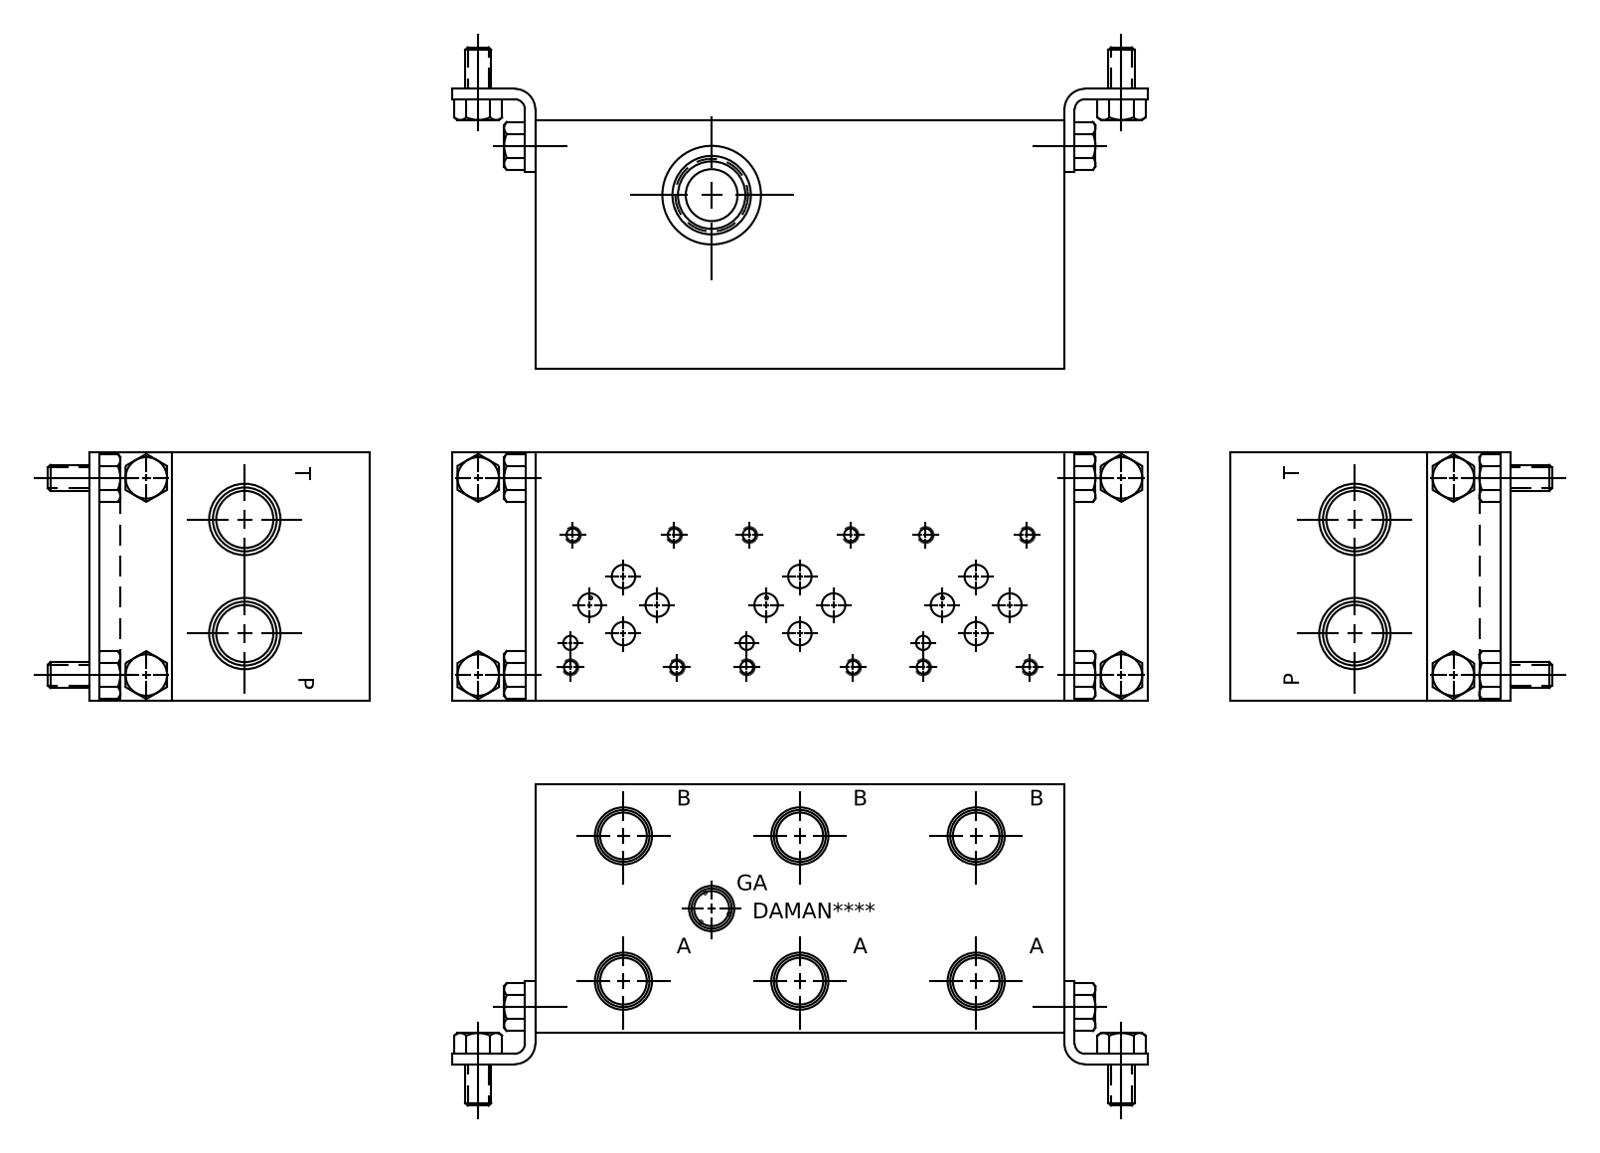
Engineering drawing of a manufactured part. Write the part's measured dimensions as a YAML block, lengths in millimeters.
part_name: "D03P032P_C"
step_written_by: "Autodesk Inventor 2021 (AUTOMOTIVE_DESIGN)"
units: millimeters
bodies: {solids: 1, faces: 681, planar: 372, cylindrical: 79, other: 230}
overall_size: [161.93, 76.2, 76.2]
volume: 859906
surface_area: 81744
round_holes:
  - {diameter: 4.22, count: 12}
  - {diameter: 5, count: 12}
  - {diameter: 7.14, count: 9}
  - {diameter: 14.3, count: 6}
  - {diameter: 17.3, count: 6}
  - {diameter: 3.96, count: 3}
  - {diameter: 6.35, count: 3}
  - {diameter: 6.76, count: 2}
  - {diameter: 8, count: 2}
  - {diameter: 15.88, count: 2}
  - {diameter: 17.48, count: 2}
  - {diameter: 21.59, count: 2}
face_to_face_distances: [76.2, 161.93, 15.37, 146.56, 11.73, 64.47, 75.41, 63.68, 0.79, 131.19]
hole_center_spacings: [53.97, 53.98, 107.95, 19.95, 22.05, 33.55, 40.49, 51.45]
